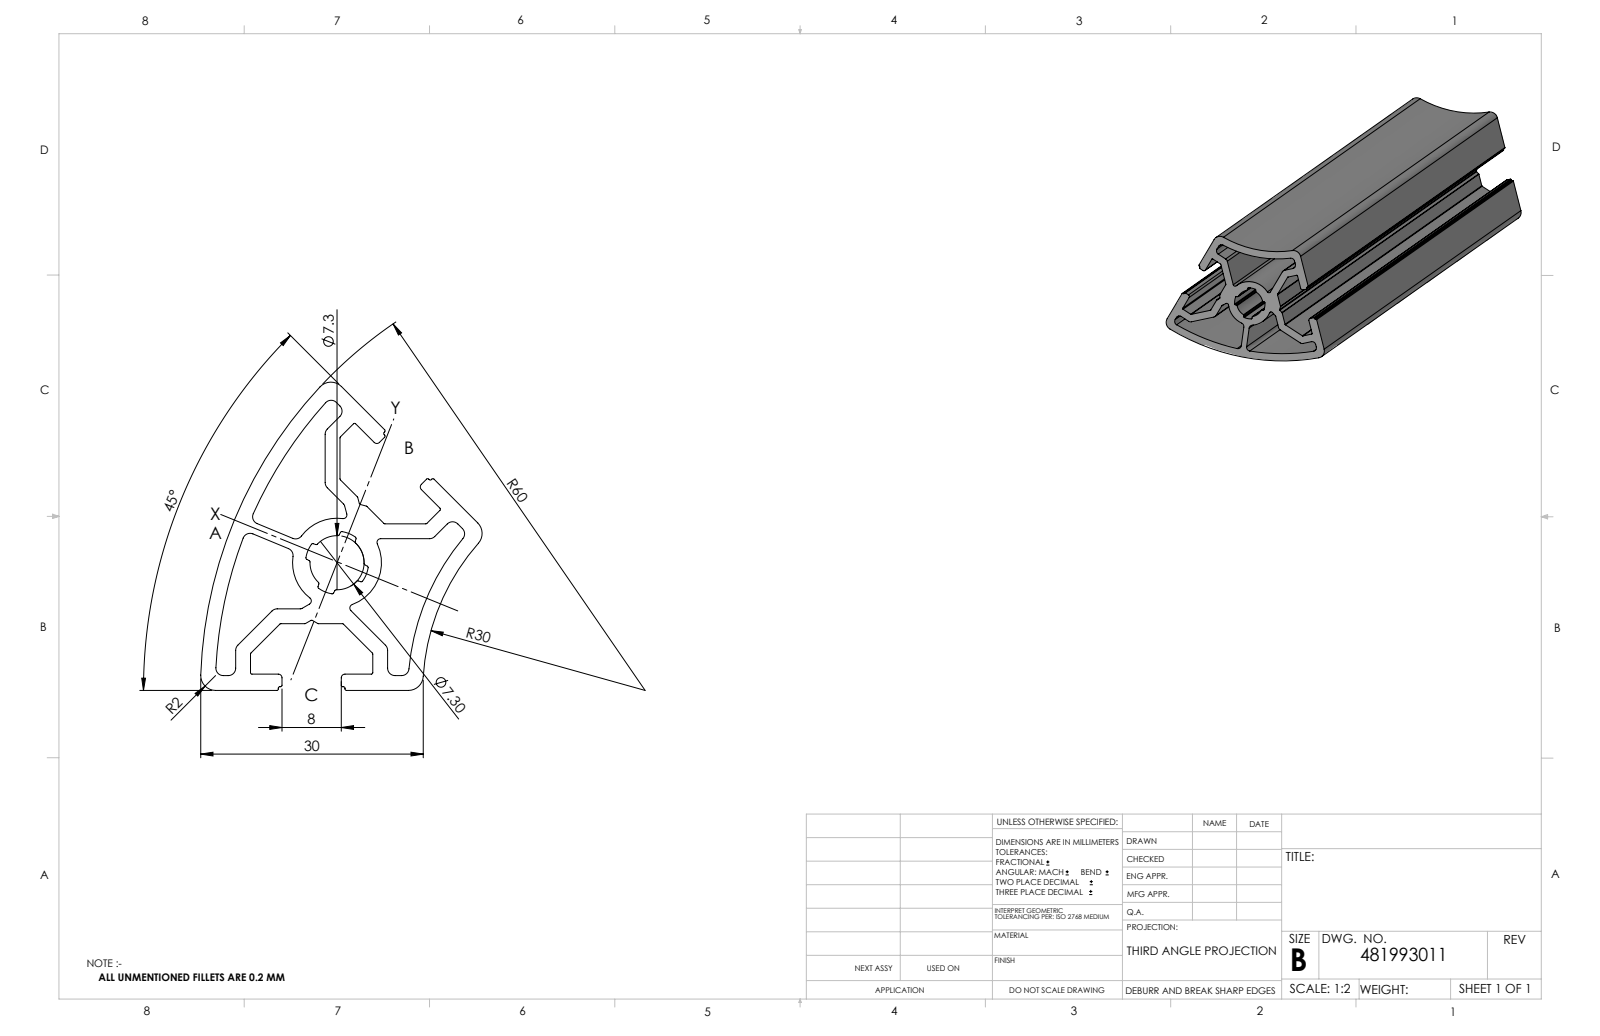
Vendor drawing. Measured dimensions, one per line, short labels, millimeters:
name: 481993011_c_1
written by: SolidWorks 2014 (CONFIG_CONTROL_DESIGN)
unit: mm
bodies: 1 solid, 172 faces (64 planar, 108 cylindrical, 0 other)
size: 200 × 41.57 × 37.97
volume: 82 489 mm³; area: 76 077 mm²
rounds: 46× R0.2, 18× R1, 10× R0.5, 4× R2, 1× R3.65, 1× R4.25, 1× R6, 1× R30
face distances: 2, 11.46, 20.46, 9, 2.2, 18.26, 6.8, 22.46, 20.26, 13.46
